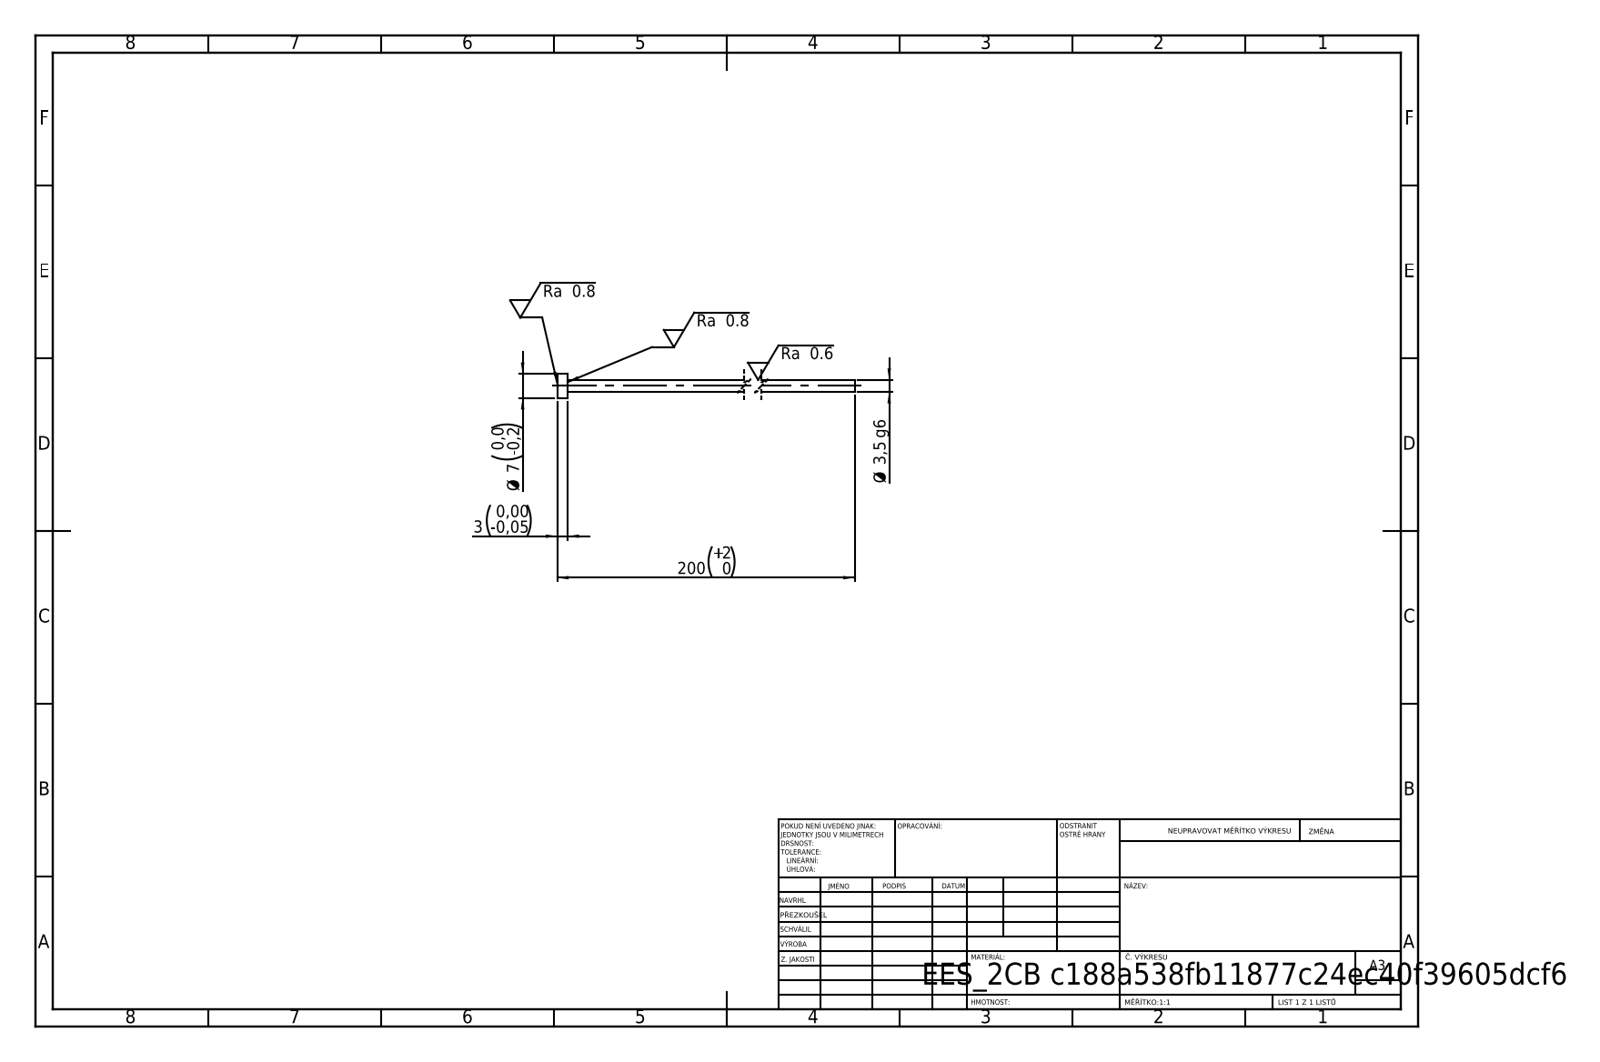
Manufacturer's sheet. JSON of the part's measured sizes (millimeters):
{"step_written_by": "SolidWorks 2019 (CONFIG_CONTROL_DESIGN)", "units": "millimeters", "bodies": {"solids": 1, "faces": 7, "planar": 3, "cylindrical": 4, "other": 0}, "overall_size": [200, 7, 7], "volume_mm3": 2011, "surface_area_mm2": 2309, "round_bosses_or_shafts": [[7, 1], [3.5, 1]], "face_to_face_distances": [3, 200, 197]}
